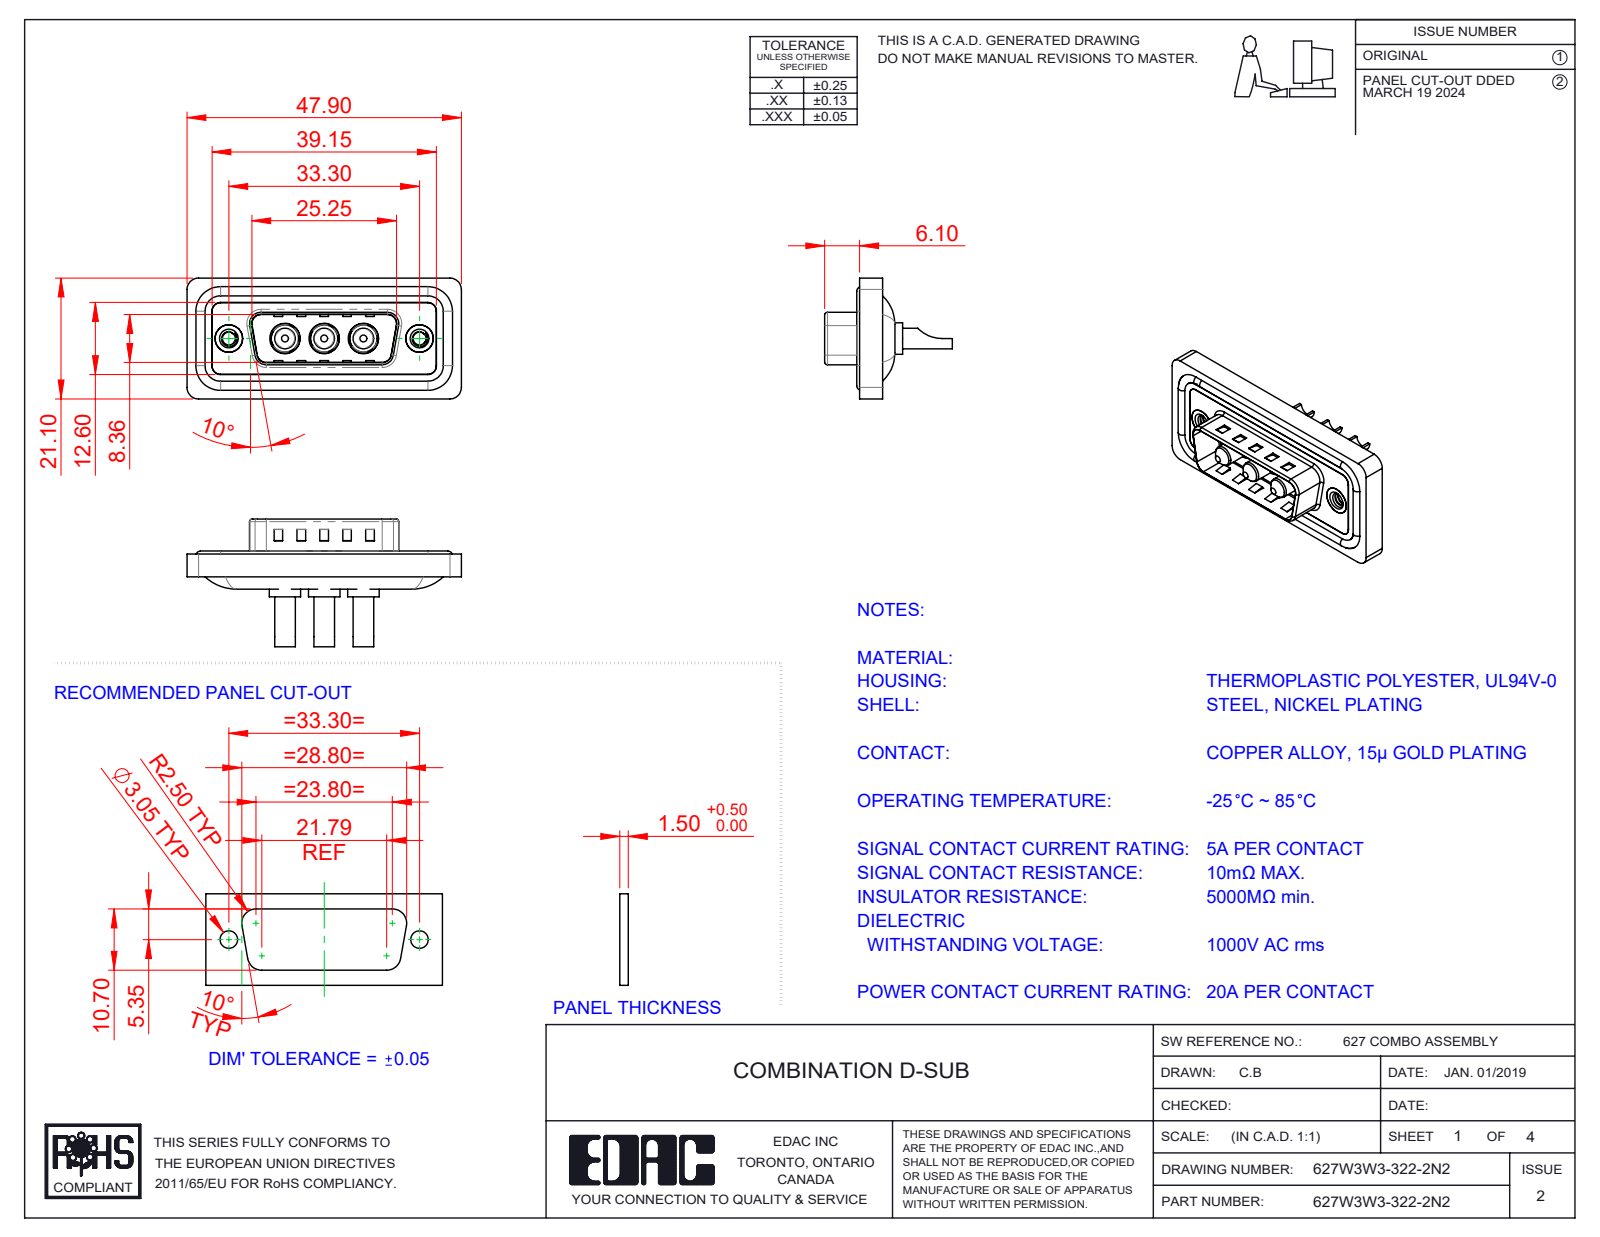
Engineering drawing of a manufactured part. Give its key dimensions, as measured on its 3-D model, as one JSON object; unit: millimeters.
{"part_name": "627Combo Threaded Rivet_2; Power Pin_20A SC; 627Combo Shell Rear_15 Contacts; 627W3W3-322-2N2 (+3 more)", "step_written_by": "SolidWorks 2023 (CONFIG_CONTROL_DESIGN)", "units": "millimeters", "bodies": {"solids": 13, "faces": 585, "planar": 216, "cylindrical": 250, "other": 119}, "overall_size": [47.9, 22.3, 21.1], "volume_mm3": 5624, "surface_area_mm2": 9001, "round_holes": [[2.7, 3], [4.85, 3], [5.3, 3], [2.26, 2], [4, 2], [4.8, 2], [5, 2]], "round_bosses_or_shafts": [[1.6, 4], [5.5, 3], [5.2, 3], [4.75, 3], [3.75, 3], [3.6, 3], [4.9, 2]], "partial_cylinders_radius": [[1.5, 26], [2, 20], [0.5, 8], [1.6, 8], [0.25, 4], [0.6, 4], [0.65, 4], [0.9, 4]], "face_to_face_distances": [0.4, 1.1, 1.5, 0.5, 1.6, 3.1, 2.9, 4, 0.82, 9.58], "hole_center_spacings": [6.85, 9.8, 16.65, 23.5, 13.7, 33.3]}
